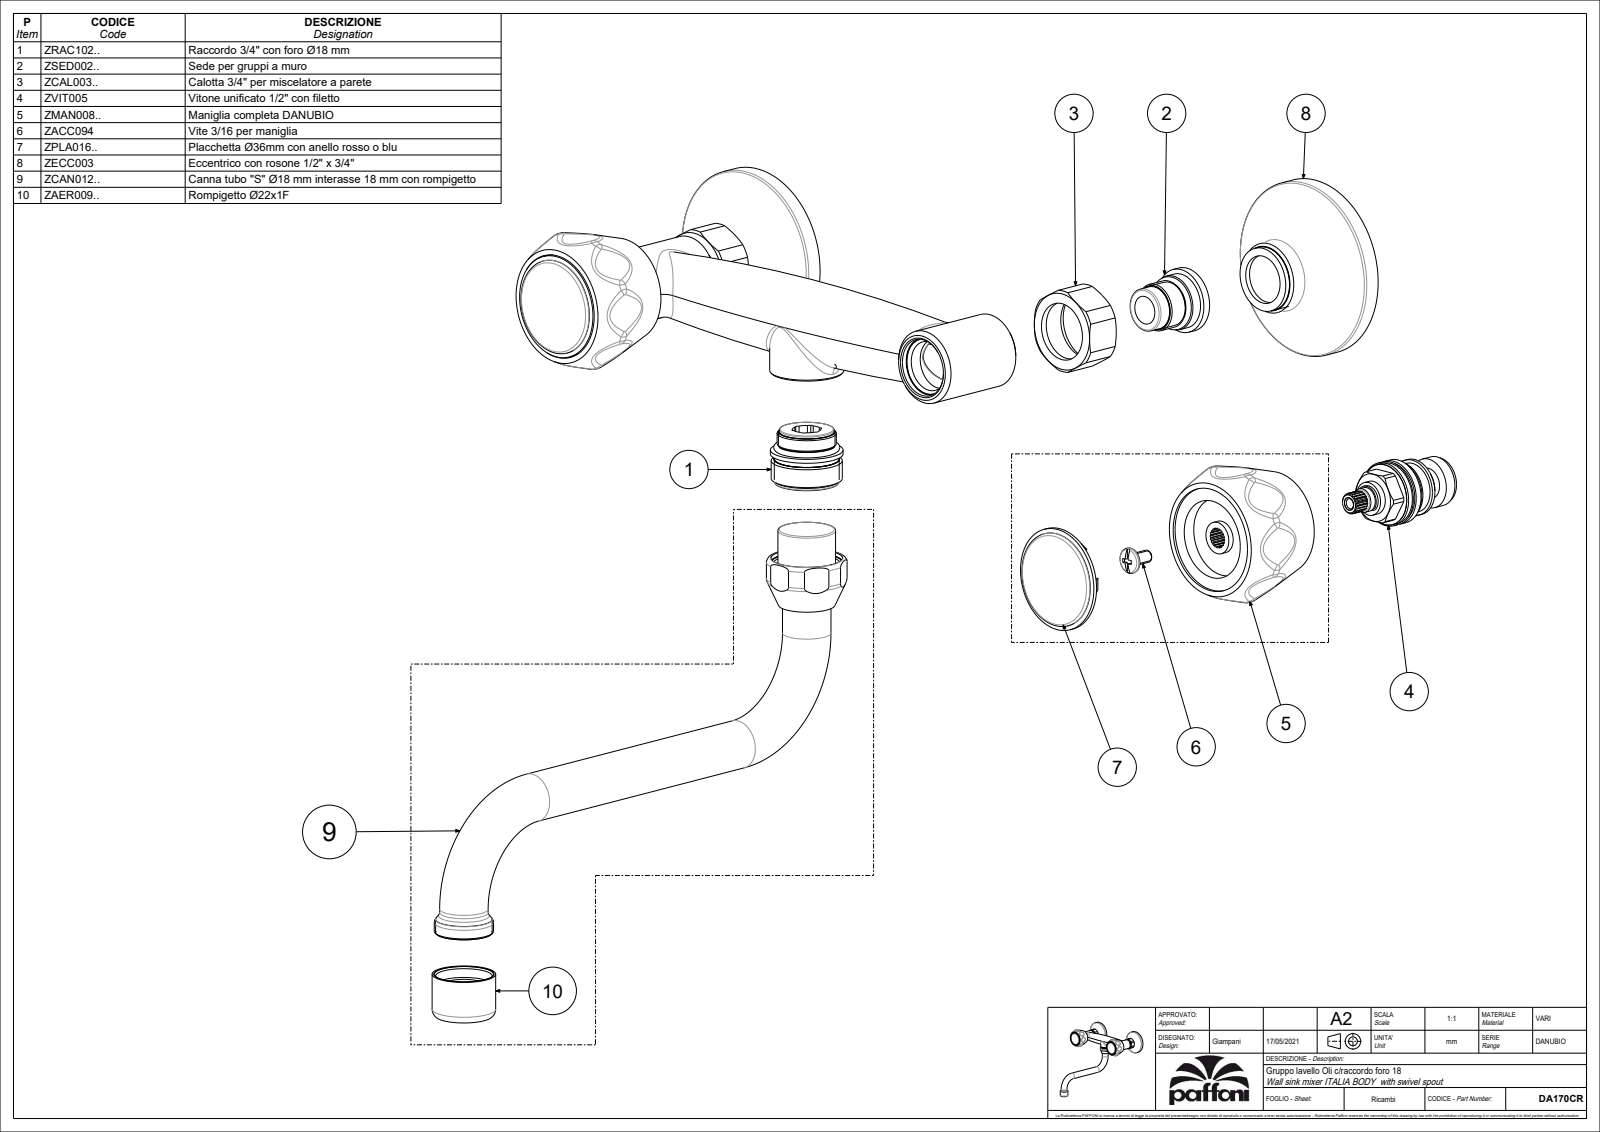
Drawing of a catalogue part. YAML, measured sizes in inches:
part_name: "DA170CR"
step_written_by: "CREO PARAMETRIC BY PTC INC, 2020044 (CONFIG_CONTROL_DESIGN)"
units: inches
bodies: {solids: 4, faces: 830, planar: 253, cylindrical: 254, other: 323}
overall_size: [9.638, 8.819, 6.935]
volume: 12.81
surface_area: 176.7
round_holes:
  - {diameter: 0.654, count: 3}
  - {diameter: 0.413, count: 2}
  - {diameter: 0.709, count: 2}
  - {diameter: 0.846, count: 2}
  - {diameter: 0.949, count: 2}
  - {diameter: 0.984, count: 2}
  - {diameter: 1.051, count: 2}
  - {diameter: 1.409, count: 2}
  - {diameter: 1.535, count: 2}
  - {diameter: 2.575, count: 2}
  - {diameter: 0.189, count: 1}
  - {diameter: 0.496, count: 1}
round_bosses_or_shafts:
  - {diameter: 1.083, count: 3}
  - {diameter: 0.945, count: 3}
  - {diameter: 0.709, count: 3}
  - {diameter: 2.598, count: 2}
  - {diameter: 1.516, count: 2}
  - {diameter: 1.201, count: 2}
  - {diameter: 1.008, count: 2}
  - {diameter: 0.886, count: 2}
partial_cylinders:
  - {radius: 0.039, count: 28}
  - {radius: 0.839, count: 16}
  - {radius: 0.118, count: 3}
  - {radius: 0.197, count: 2}
  - {radius: 0.394, count: 2}
  - {radius: 0.61, count: 2}
  - {radius: 0.207, count: 1}
  - {radius: 0.307, count: 1}
face_to_face_distances: [1.142, 0.374, 1.969, 3.11, 0.264, 1.39, 2.465, 2.728, 0.39, 2.839]
hole_center_spacings: [4.605, 6.22, 7.087]
